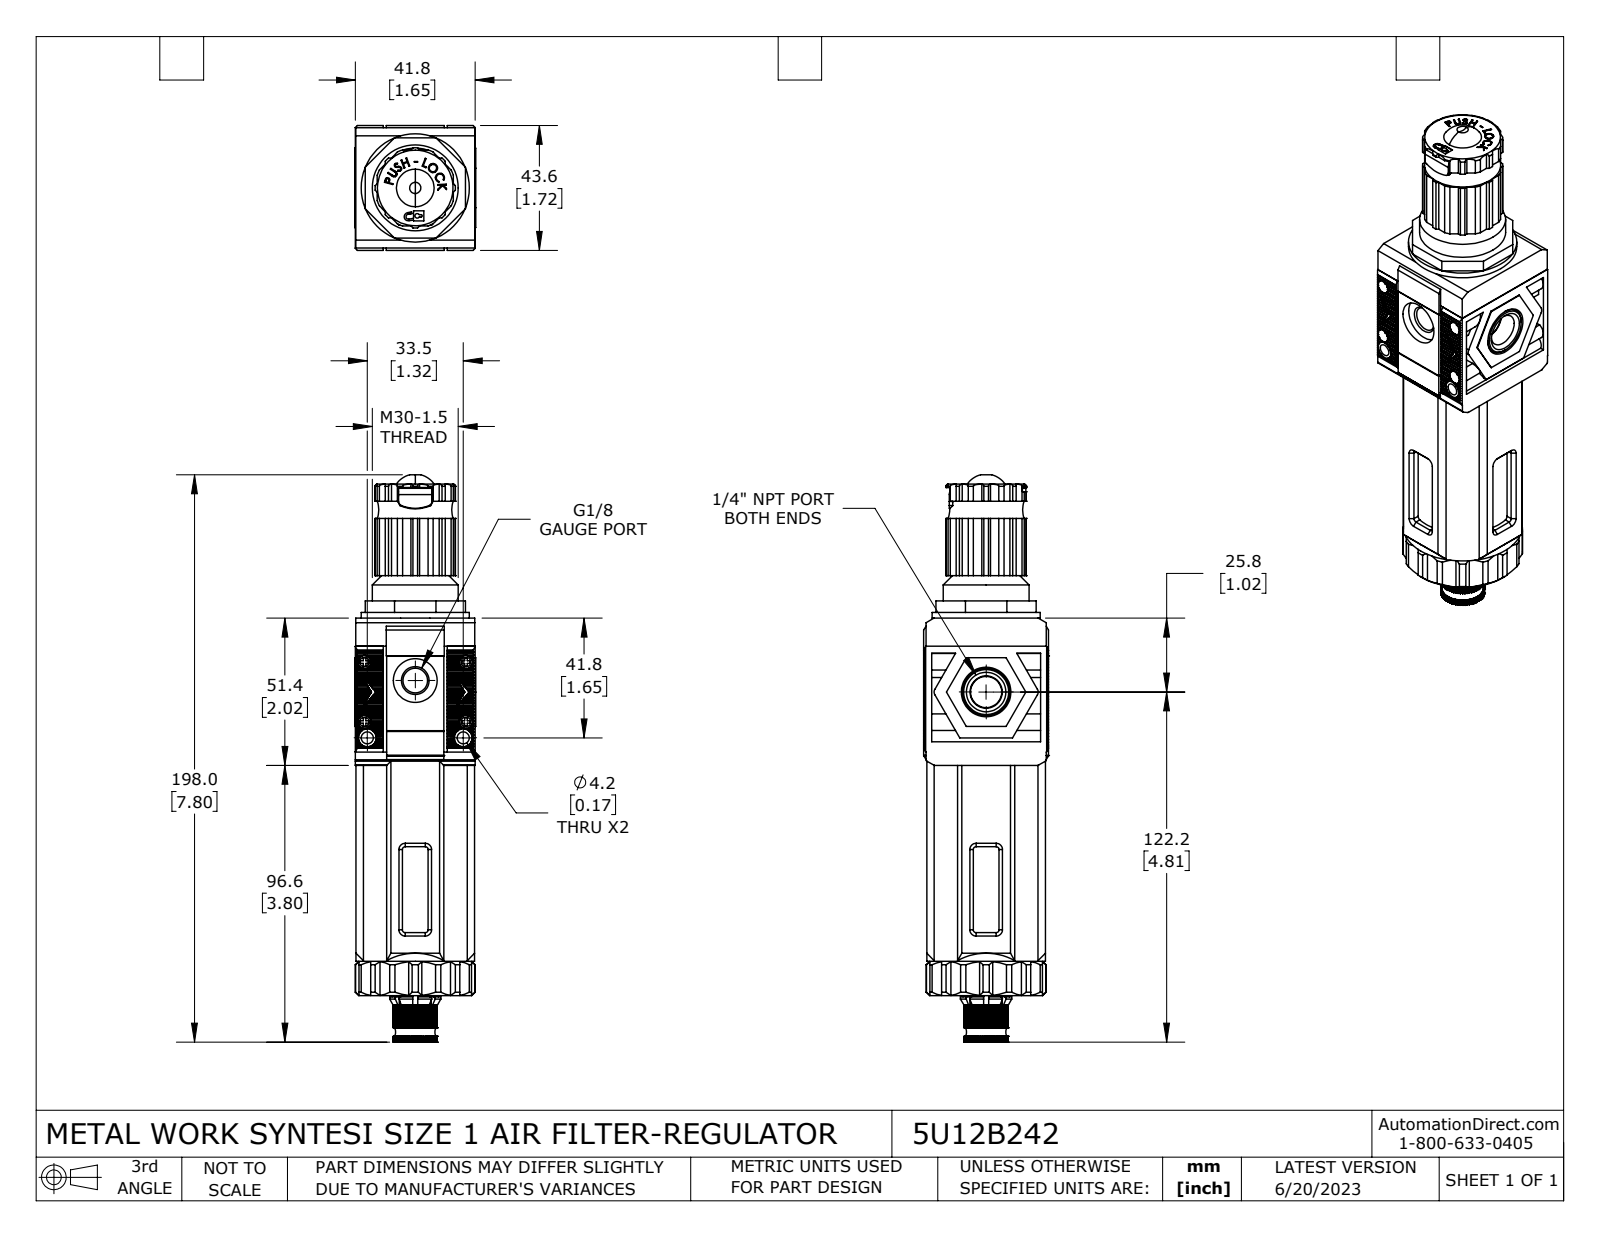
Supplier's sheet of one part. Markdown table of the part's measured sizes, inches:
| quantity | value |
| --- | --- |
| part name | 5U12B242 |
| STEP written by | SolidWorks 2021 (CONFIG_CONTROL_DESIGN) |
| units | inches |
| bodies | 15 solids, 2181 faces (1612 planar, 418 cylindrical, 151 other) |
| overall size | 7.795 × 1.717 × 1.661 |
| volume | 9.849 in³ |
| surface area | 115.2 in² |
| round holes (diameter × count) | 0.083 × 4, 0.118 × 4, 0.185 × 4, 0.138 × 2, 0.165 × 2, 0.094 × 1, 0.126 × 1, 0.252 × 1, 0.276 × 1, 0.337 × 1, 0.343 × 1, 0.602 × 1 |
| round bosses / shafts (diameter × count) | 0.181 × 4, 0.102 × 4, 0.244 × 2, 1.63 × 1, 1.488 × 1, 1.402 × 1, 0.984 × 1, 0.898 × 1 |
| partial cylindrical surfaces (radius × count) | 0.039 × 9, 0.024 × 4, 0.122 × 4, 0.059 × 3, 0.008 × 2, 0.051 × 2, 0.079 × 2, 0.016 × 1 |
| main face-to-face distances | 1.638, 1.63, 0.043, 1.673, 1.646, 0.307, 1.339, 1.642, 0.299, 1.331 |
| hole center spacings | 0.222, 0.362, 0.742, 0.785, 0.823, 0.9, 1.027, 1.042 |
